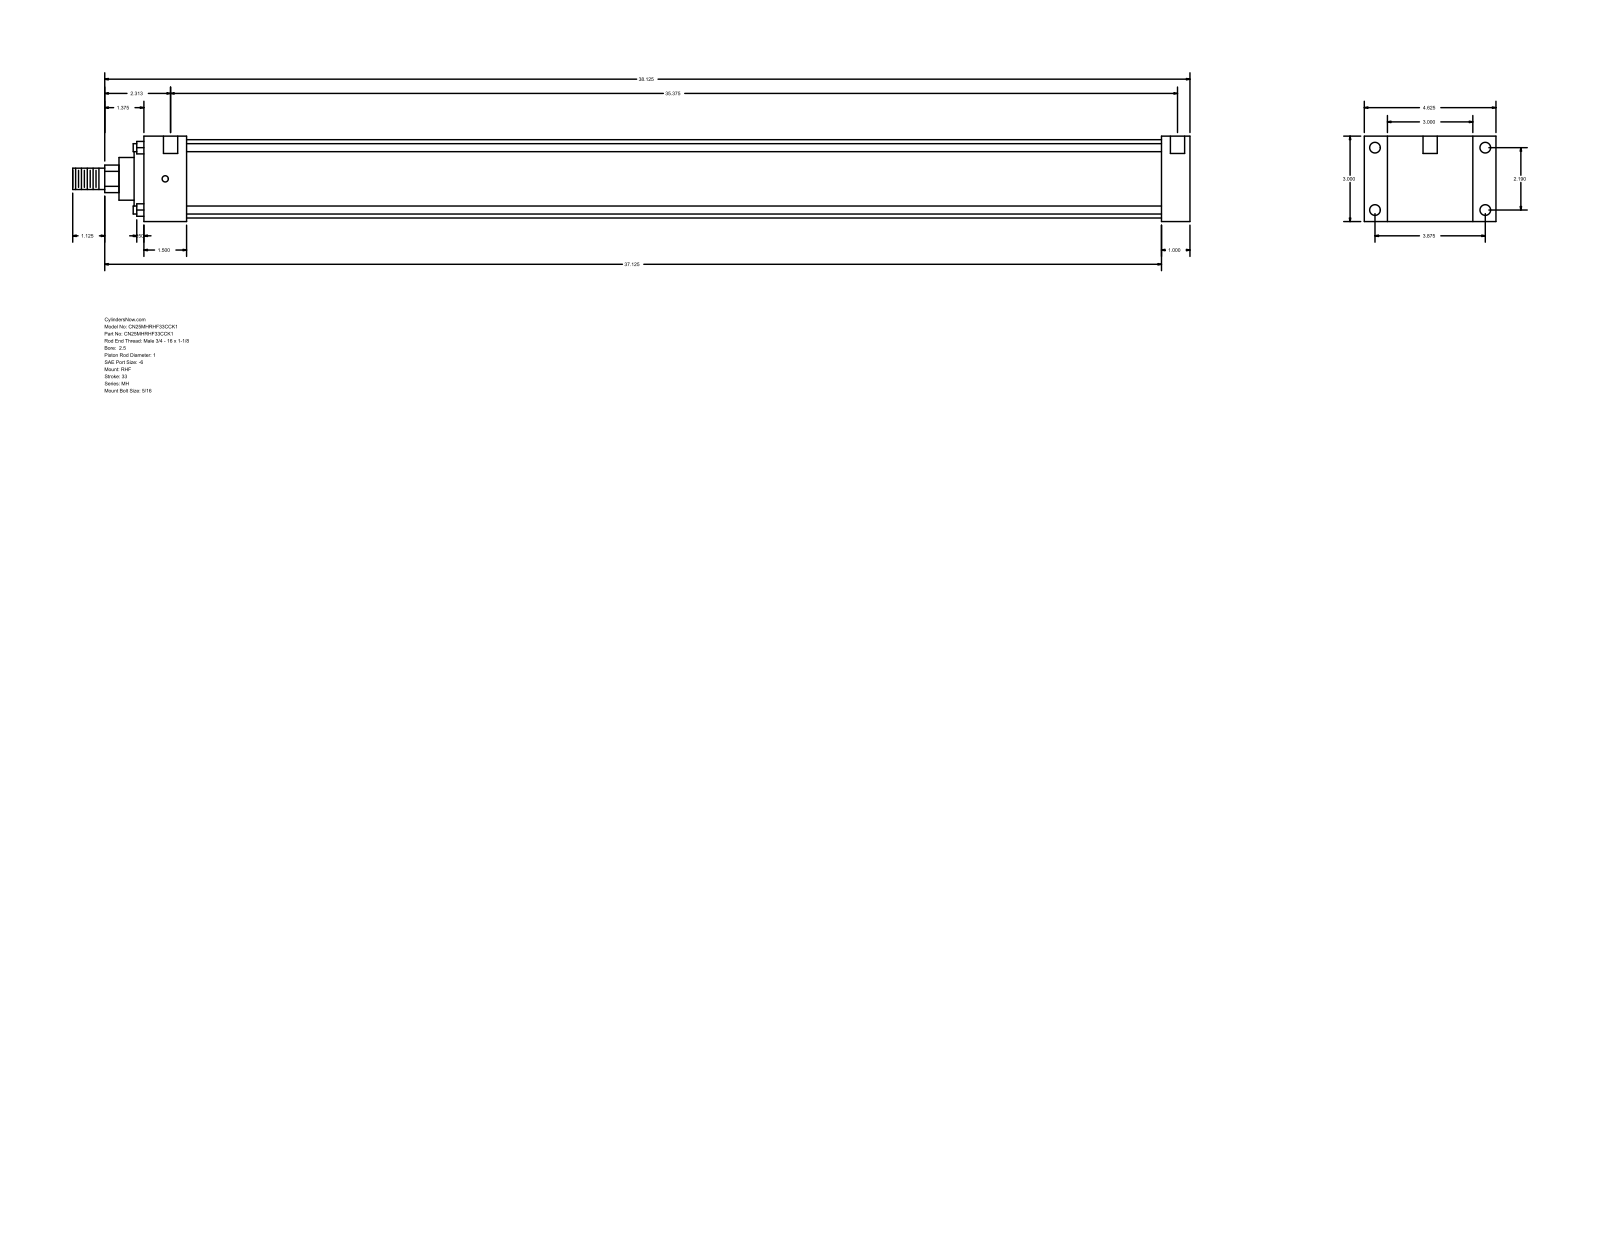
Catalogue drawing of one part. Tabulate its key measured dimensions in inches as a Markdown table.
| quantity | value |
| --- | --- |
| part name | MH_RHF__0250_1 |
| STEP written by | GSSL Pune (CONFIG_CONTROL_DESIGN) |
| units | inches |
| bodies | 0 solids, 90 faces (61 planar, 29 cylindrical, 0 other) |
| overall size | 39.25 × 4.625 × 3 |
| round holes (diameter × count) | 0.219 × 4, 0.375 × 4, 0.5 × 2 |
| round bosses / shafts (diameter × count) | 0.281 × 4, 2.75 × 1, 2.375 × 1, 1.5 × 1, 1 × 1, 0.75 × 1 |
| partial cylindrical surfaces (radius × count) | 0.484 × 1 |
| main face-to-face distances | 3, 1, 0.813, 3.813, 35.75, 36.75, 4.625, 1.5, 34.25, 35.25 |
| hole center spacings | 2.19, 3.875, 4.451, 35.687, 0.125, 0.187, 35.375, 35.5 |
